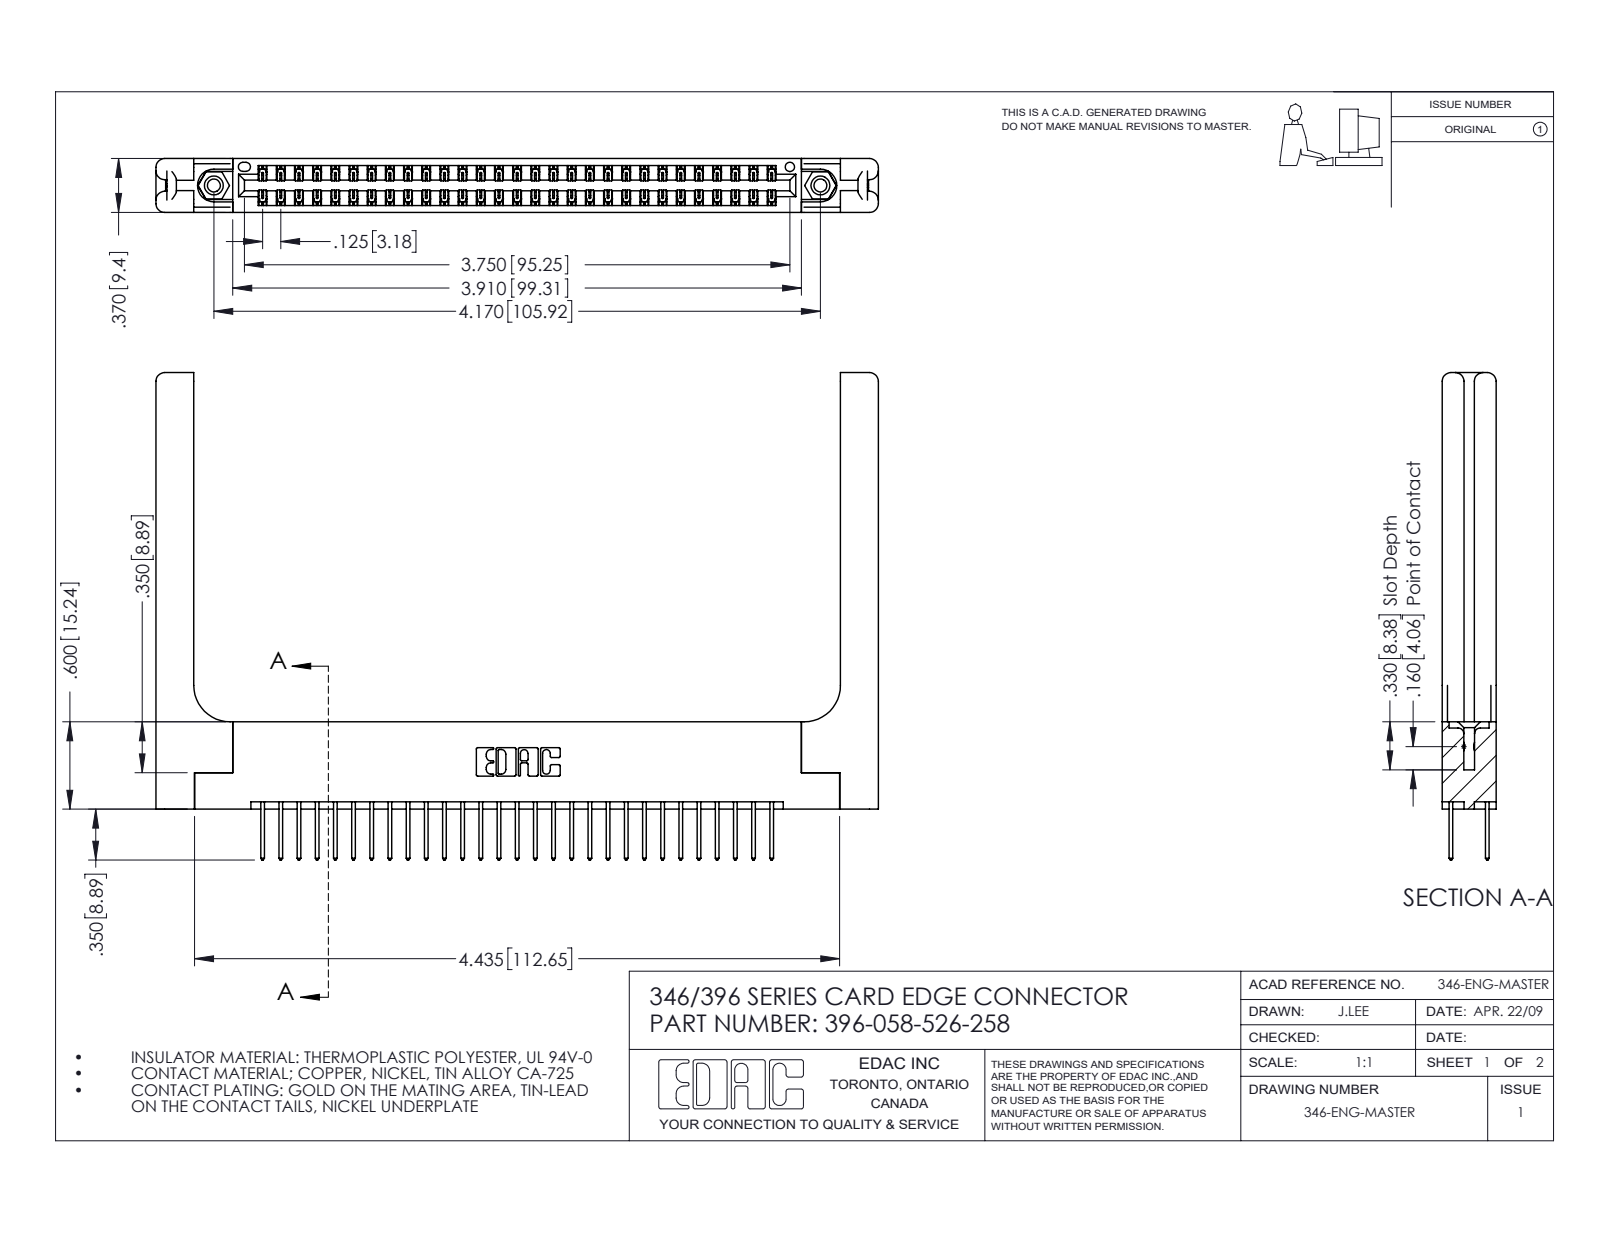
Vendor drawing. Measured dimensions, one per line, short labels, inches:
name: 345-250-001_345-250-001-102; 346 Part_Flush Mounting Lugs - 0.156 Dia-TH; 345-292-001_345-293-126; 346-220-058_345-220-058 (+1 more)
written by: SolidWorks 2016 (CONFIG_CONTROL_DESIGN)
unit: in
bodies: 63 solids, 3394 faces (2254 planar, 1080 cylindrical, 60 other)
size: 4.966 × 3.35 × 0.37
volume: 1.208 in³; area: 34.24 in²
holes: 2× ⌀0.089, 2× ⌀0.125, 2× ⌀0.156, 1× ⌀0.064
bosses: 2× ⌀0.155
rounds: 87× R0.006, 58× R0.01, 22× R0.01, 16× R0.06, 6× R0.007, 6× R0.031, 3× R0.026, 2× R0.014
face distances: 0.37, 0.048, 0.322, 0.072, 0.25, 0.15, 0.148, 0.025, 0.298, 0.275
hole spacings: 0.246, 3.962, 4.17
